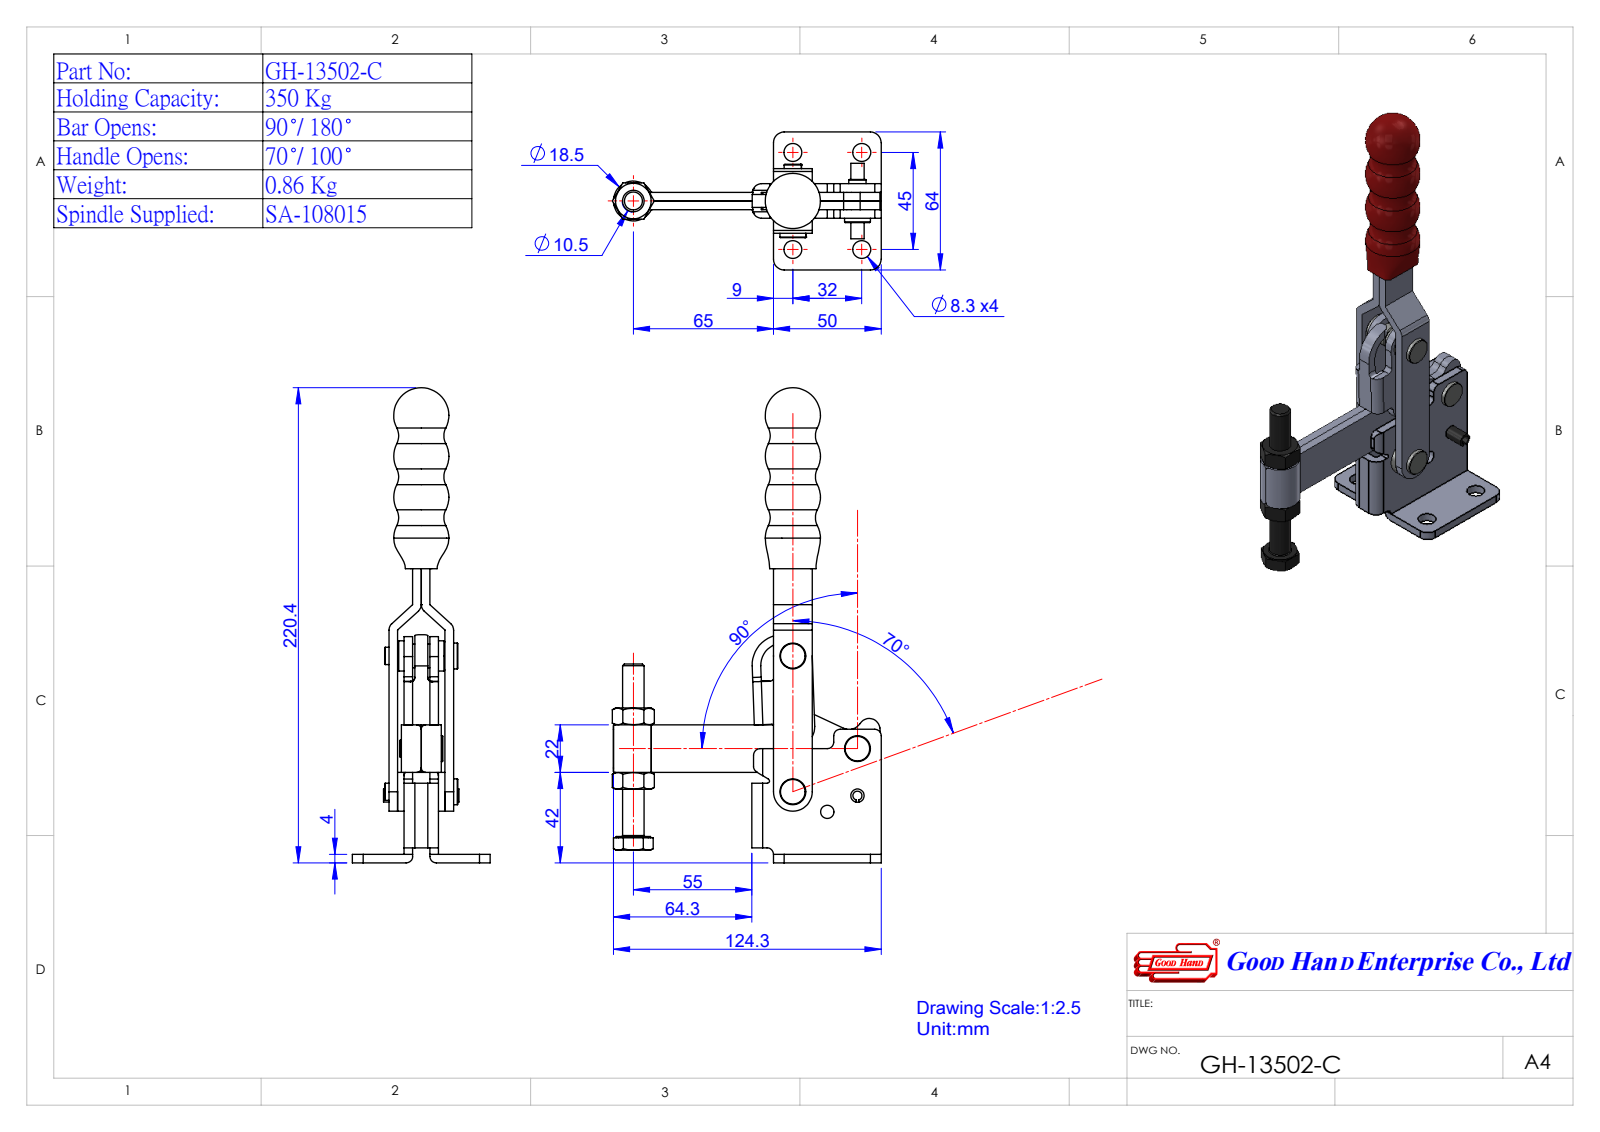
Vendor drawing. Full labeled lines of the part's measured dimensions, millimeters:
Part name (STEP PRODUCT): GH-SA-108015-1^GH-13502-C(簡化); Group2^GH-13502-C(簡化); GH-13502-C(簡化); Group4^GH-13502-B(簡化) (+2 more)
STEP written by: SolidWorks 2016 (AUTOMOTIVE_DESIGN)
Units: millimetres
Bodies: 4 solids, 306 faces (107 planar, 125 cylindrical, 74 other)
Overall size (bounding box): 220.4 × 124.81 × 64
Volume: 135 510 mm³ · Surface area: 61 418 mm²
Round holes (diameter × count): ⌀6 ×5, ⌀8.3 ×4, ⌀8.5 ×1, ⌀10 ×1
Round bosses / shafts (diameter × count): ⌀12 ×4, ⌀18.5 ×1, ⌀6 ×1
Partial cylindrical surfaces — rounded edges, fillets, slot ends (radius × count): R5 ×7, R3 ×5, R9 ×5, R4.1 ×4, R1 ×2, R2 ×2, R0.1 ×1, R6 ×1
Main face-to-face distances: 4, 8, 12, 11, 7, 15, 19, 16, 26, 23
Hole centre spacings: 32, 45, 55.22, 77.35, 108.36, 18.52, 30.04, 30.54
